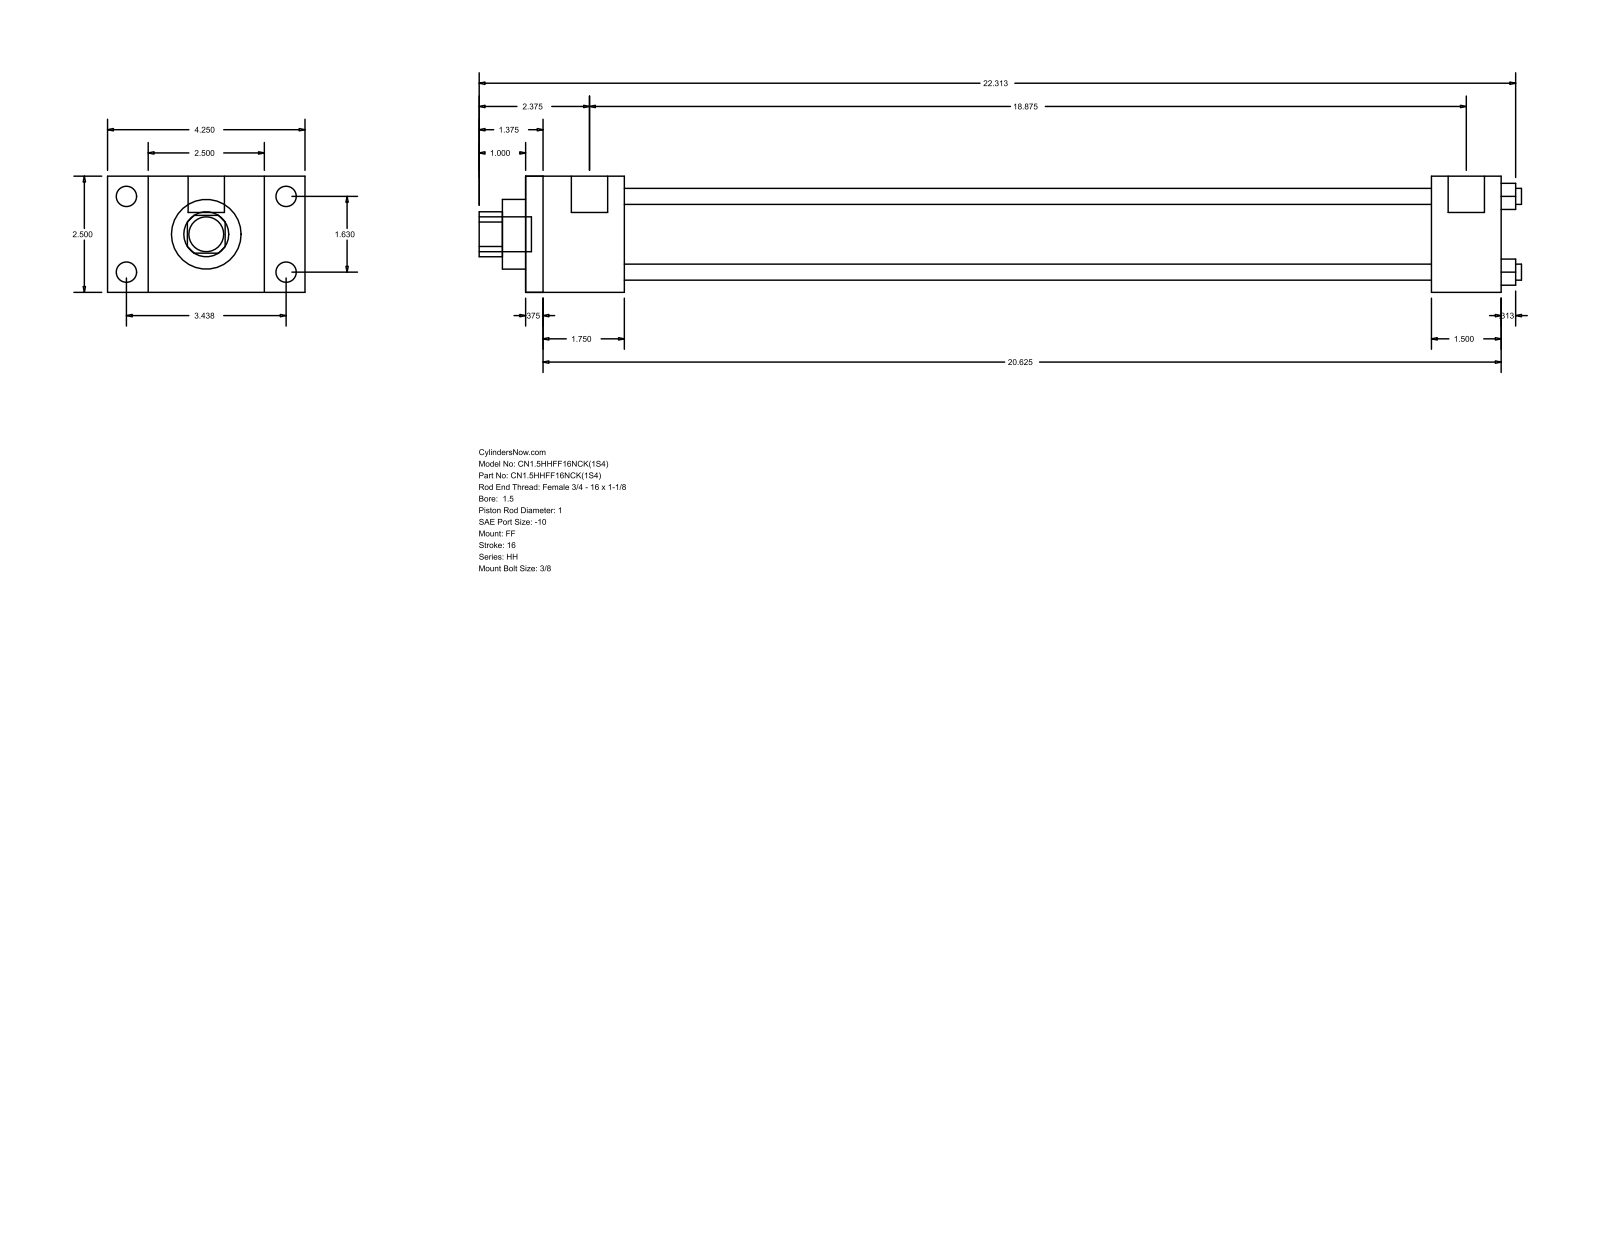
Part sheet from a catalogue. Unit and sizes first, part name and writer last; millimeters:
Units: millimetres
Overall size (bounding box): 569.91 × 107.95 × 63.5
Round holes (diameter × count): ⌀8.76 ×4, ⌀25.4 ×1, ⌀38.1 ×1, ⌀44.45 ×1
Round bosses / shafts (diameter × count): ⌀11.13 ×4, ⌀5.56 ×4, ⌀19.84 ×2, ⌀19.05 ×1
Partial cylindrical surfaces — rounded edges, fillets, slot ends (radius × count): R12.29 ×1
Main face-to-face distances: 63.5, 533.4, 9.52, 523.88, 53.98, 44.46, 479.42, 495.3, 485.78, 441.32
Hole centre spacings: 29.27, 41.4, 58.55
Bodies: 0 solids, 92 faces (64 planar, 28 cylindrical, 0 other)
Part name (STEP PRODUCT): HH_FF__0150_1
STEP written by: GSSL Pune (CONFIG_CONTROL_DESIGN)
